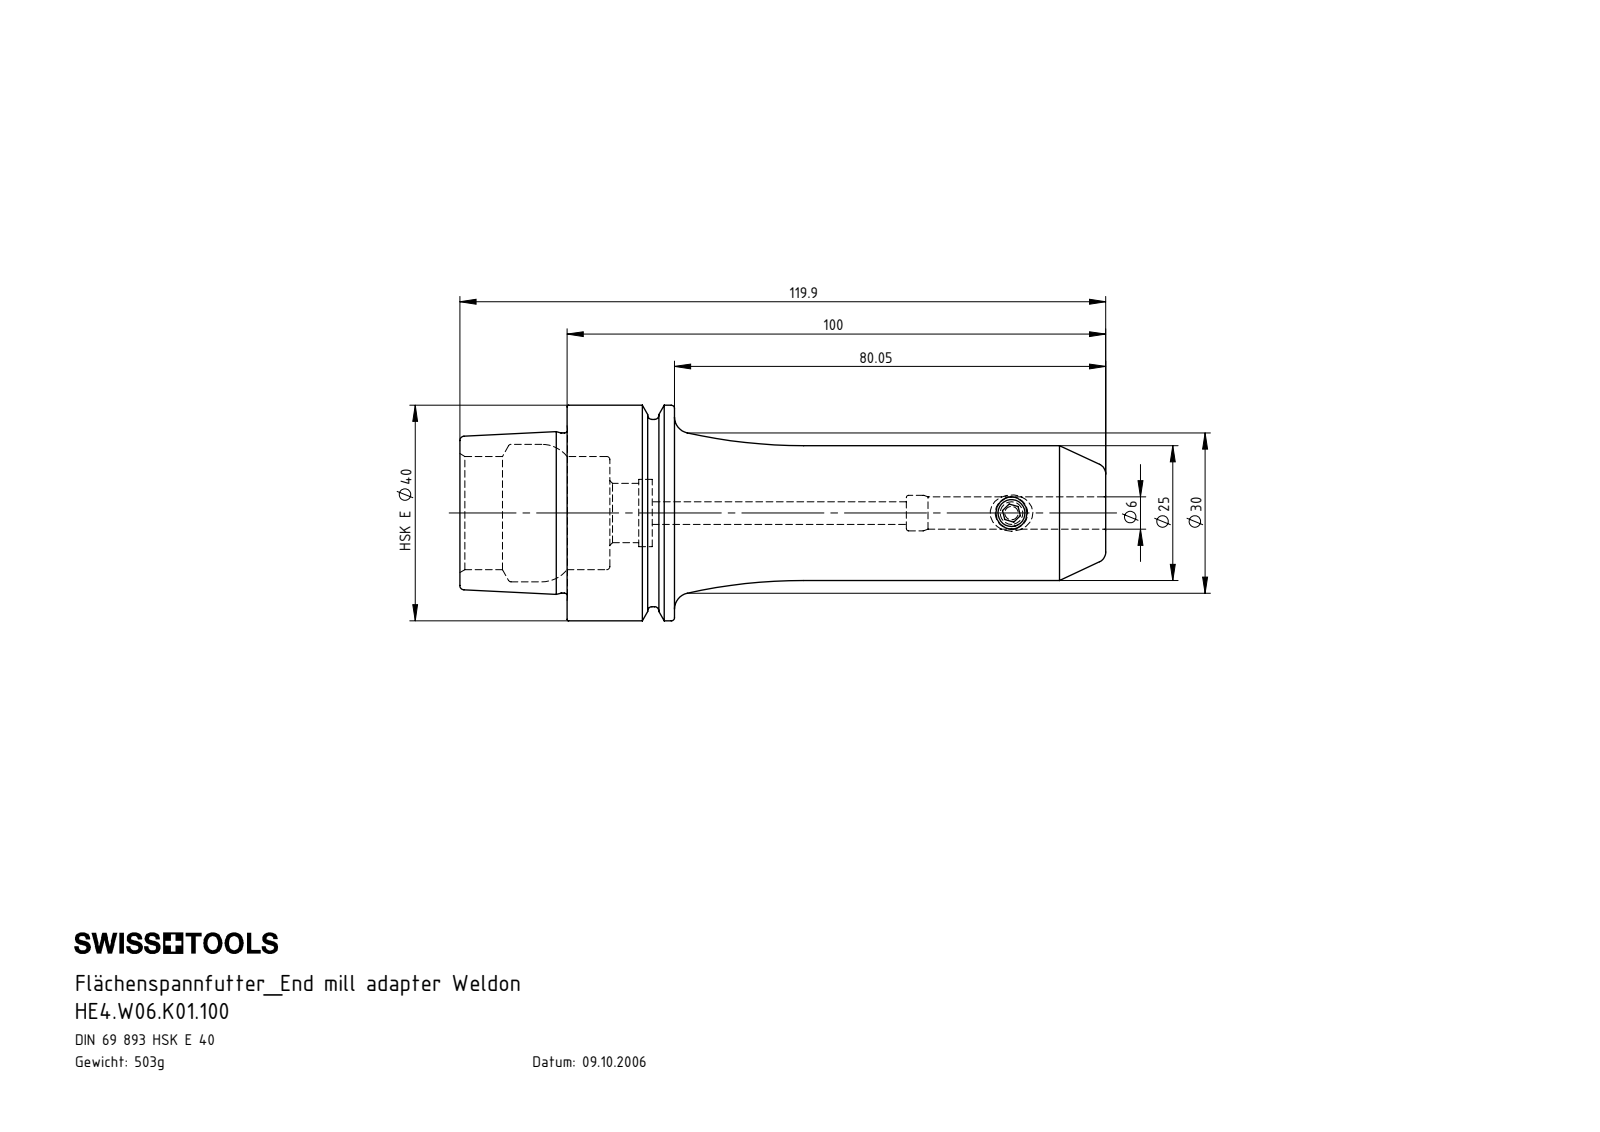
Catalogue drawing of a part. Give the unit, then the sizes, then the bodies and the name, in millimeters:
Units: millimetres
Overall size (bounding box): 119.9 × 40 × 40
Round holes (diameter × count): ⌀4.2 ×1, ⌀5 ×1, ⌀6 ×1, ⌀6.6 ×1, ⌀11 ×1, ⌀12.5 ×1, ⌀21 ×1, ⌀25.5 ×1
Round bosses / shafts (diameter × count): ⌀40 ×1, ⌀34.75 ×1, ⌀29.71 ×1, ⌀25 ×1, ⌀6 ×1
Main face-to-face distances: 7.95, 19.95, 12, 19.9, 27.85, 39.85, 119.9, 100, 92.05, 80.05
Volume: 64 061 mm³ · Surface area: 16 928 mm²
Bodies: 2 solids, 113 faces (19 planar, 30 cylindrical, 64 other)
Part name (STEP PRODUCT): HE4.W06.K01.100; HE4-W06.K01.100_B_Fertigbearbeitung; W06-ER1.001.010
STEP written by: SolidWorks 2017 (CONFIG_CONTROL_DESIGN)
